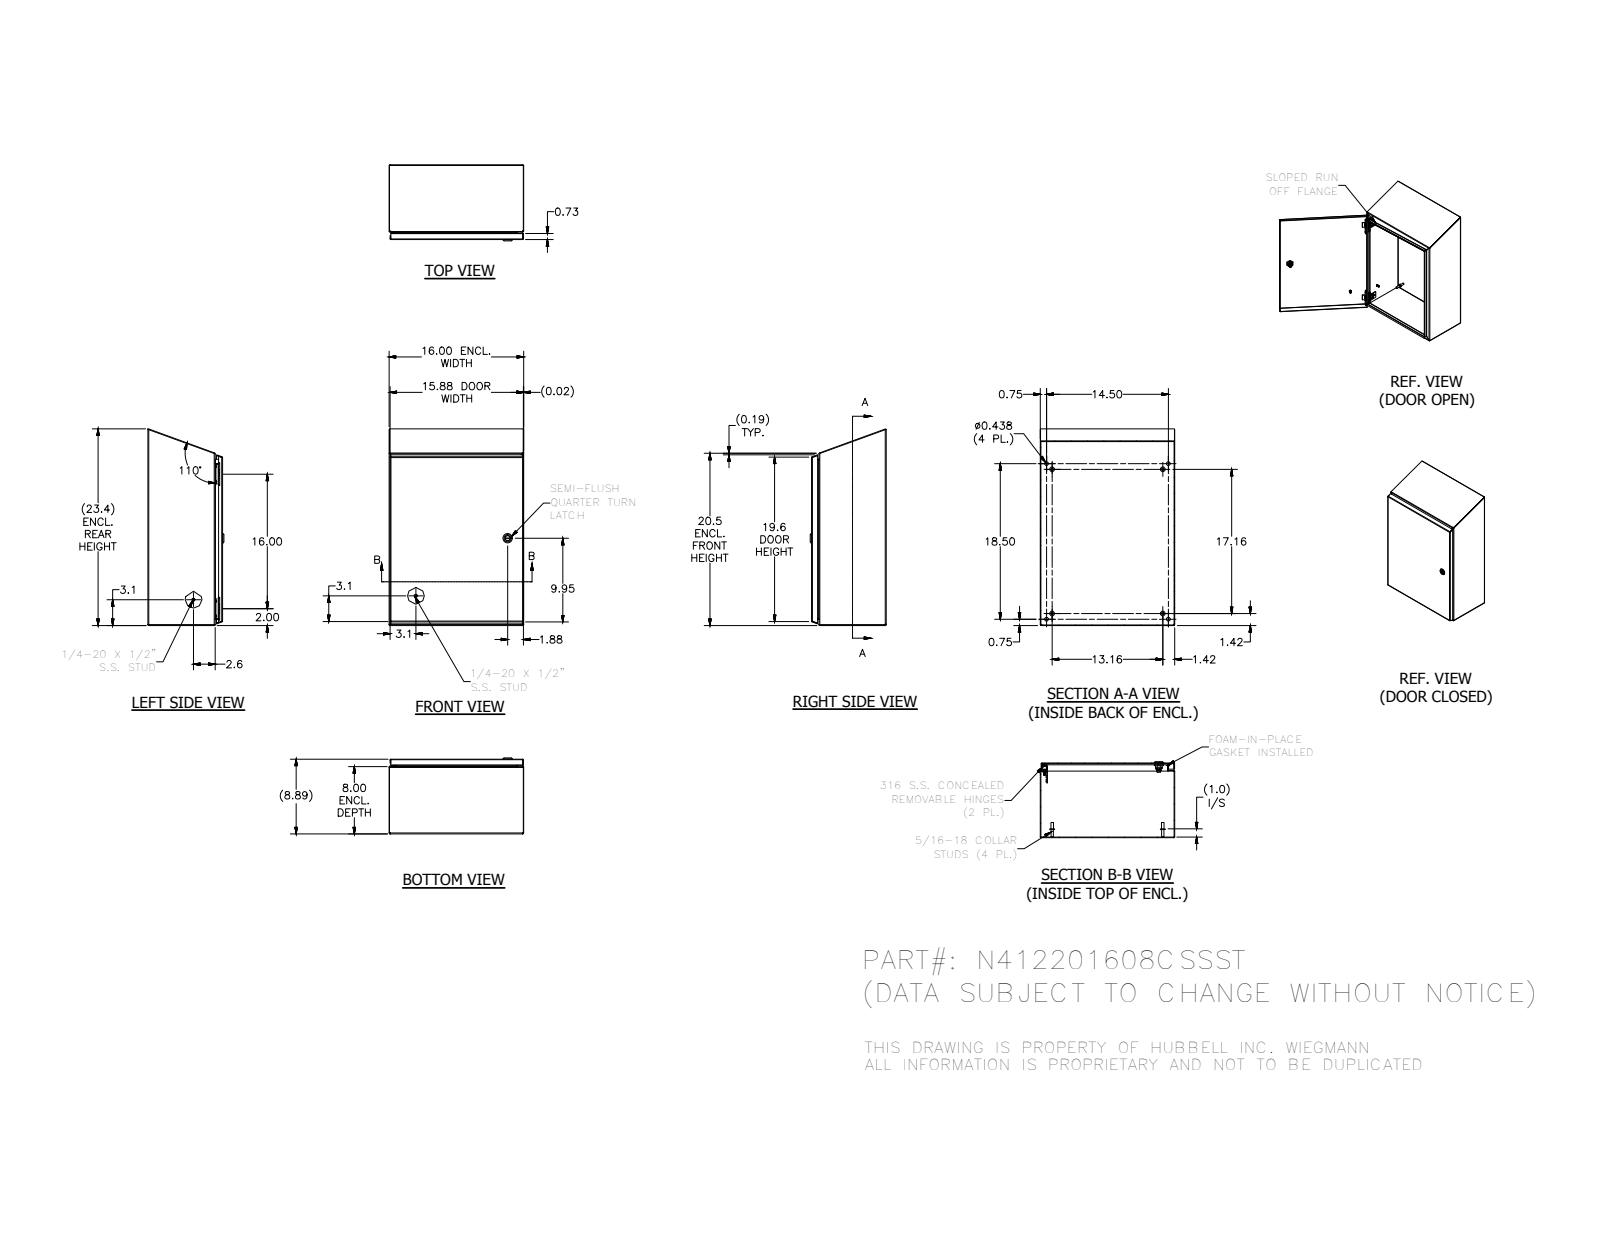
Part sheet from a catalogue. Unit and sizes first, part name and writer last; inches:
Units: inches
Overall size (bounding box): 23.391 × 16 × 9.044
Round holes (diameter × count): ⌀0.093 ×4, ⌀0.152 ×4, ⌀0.167 ×4, ⌀0.172 ×4, ⌀0.187 ×4, ⌀0.437 ×4, ⌀0.156 ×3, ⌀0.187 ×1, ⌀0.197 ×1, ⌀0.315 ×1, ⌀0.394 ×1, ⌀0.402 ×1
Round bosses / shafts (diameter × count): ⌀0.25 ×10, ⌀0.563 ×4, ⌀0.36 ×4, ⌀0.32 ×4, ⌀0.3 ×4, ⌀0.275 ×4, ⌀0.256 ×4, ⌀0.164 ×4
Partial cylindrical surfaces — rounded edges, fillets, slot ends (radius × count): R0.031 ×29, R0.05 ×26, R0.105 ×19, R0.016 ×18, R0.02 ×16, R0.125 ×16, R0.032 ×8, R0.524 ×6
Main face-to-face distances: 0.074, 8.813, 15.926, 8.739, 8.887, 16, 15.852, 7.926, 0.887, 0.813
Hole centre spacings: 16, 14.774, 0.5, 0.656, 0.66, 0.952, 1.307, 1.311
Volume: 108.2 in³ · Surface area: 2 946 in²
Bodies: 36 solids, 1426 faces (538 planar, 509 cylindrical, 379 other)
Part name (STEP PRODUCT): N412201608CSSST
STEP written by: SolidWorks 2018 (AUTOMOTIVE_DESIGN)
